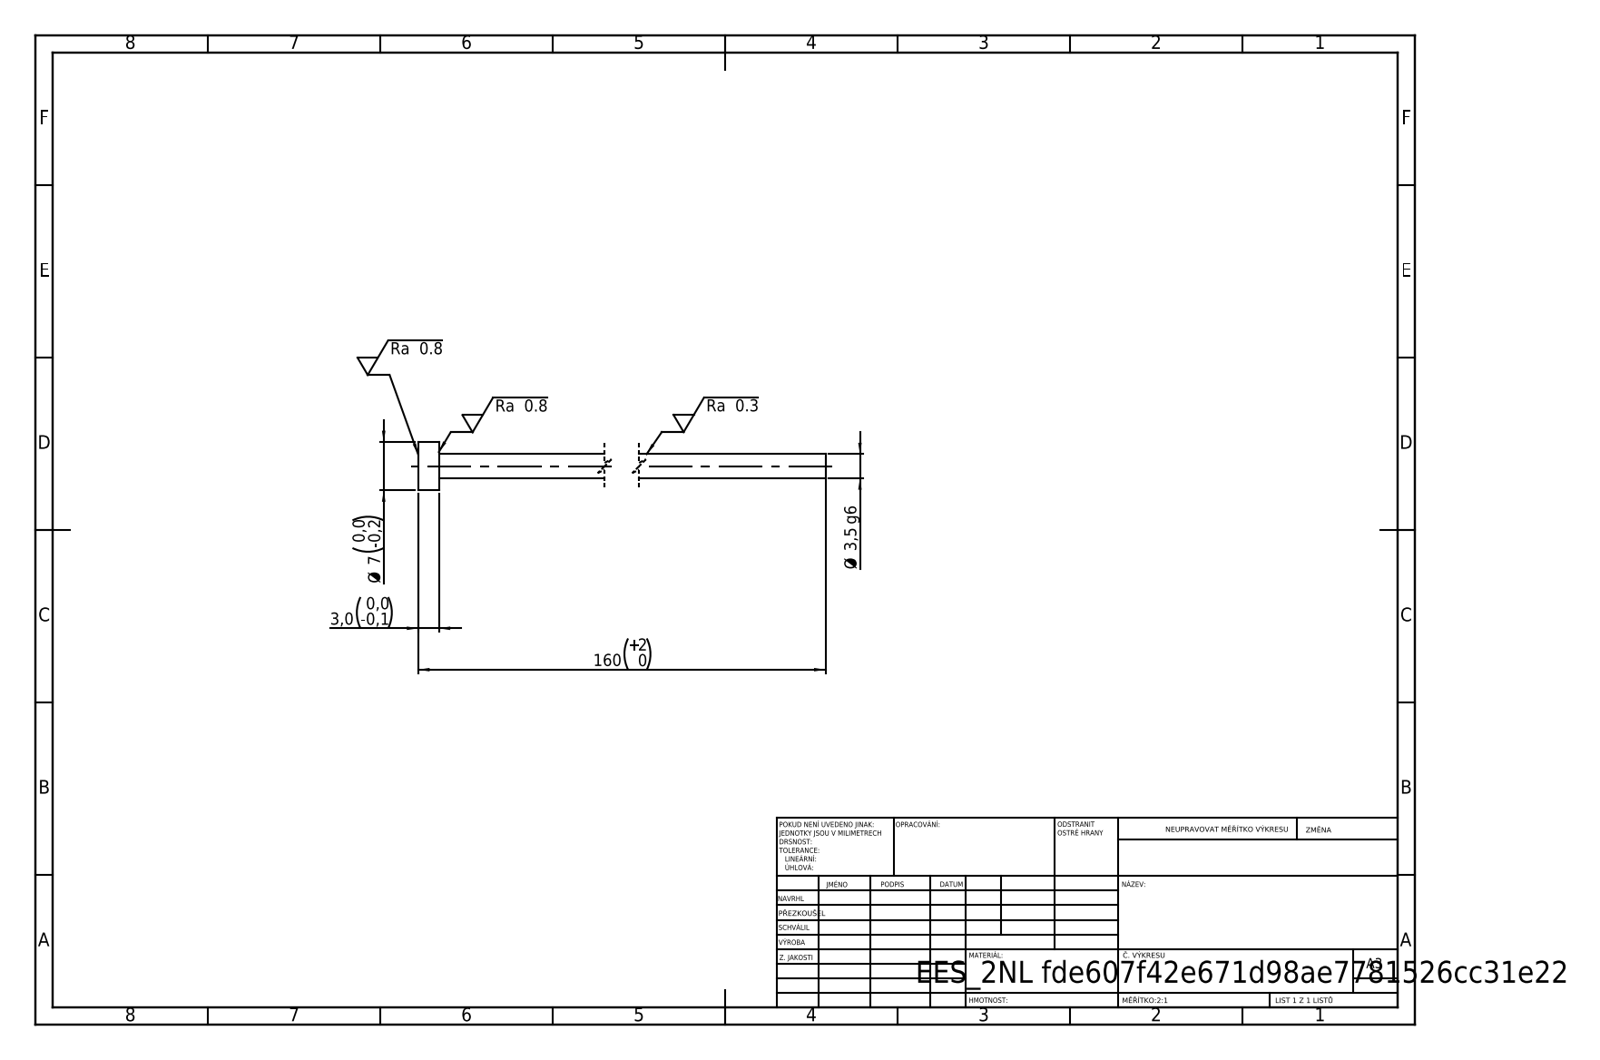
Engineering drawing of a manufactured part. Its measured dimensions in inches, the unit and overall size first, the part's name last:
Units: inches
Overall size (bounding box): 6.299 × 0.276 × 0.276
Round bosses / shafts (diameter × count): ⌀0.276 ×1, ⌀0.138 ×1
Main face-to-face distances: 0.118, 6.299, 6.181
Volume: 0.099 in³ · Surface area: 2.897 in²
Bodies: 1 solid, 7 faces (3 planar, 4 cylindrical, 0 other)
STEP written by: SolidWorks 2019 (CONFIG_CONTROL_DESIGN)
